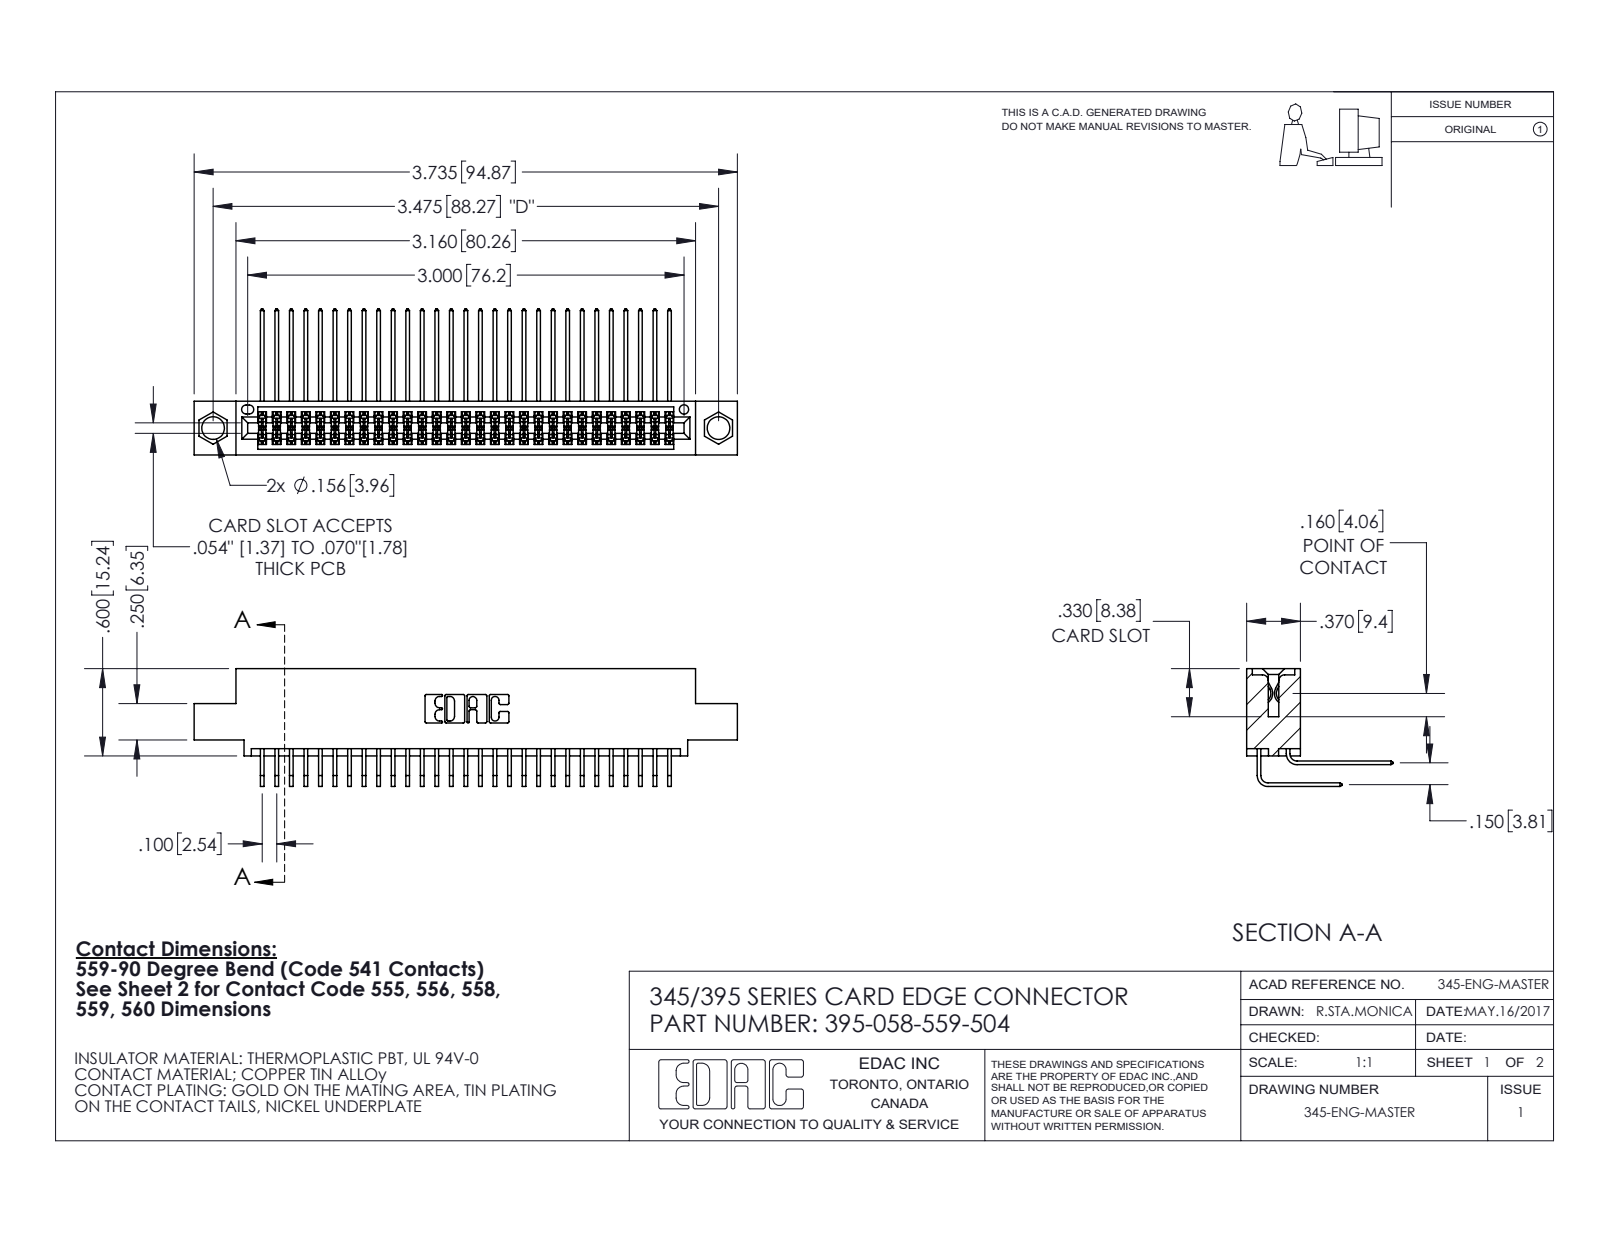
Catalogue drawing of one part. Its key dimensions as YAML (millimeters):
part_name: "395-058-559-504; 345-292-001_558 559 Tail - 1; 345-292-001_559 Tail - 2; 345 Part_0.110 Offset - 0.156 Dia-TI"
step_written_by: "SolidWorks 2020 (CONFIG_CONTROL_DESIGN)"
units: millimeters
bodies: {solids: 59, faces: 3160, planar: 2128, cylindrical: 1032, other: 0}
overall_size: [94.9, 25.5, 20.5]
volume: 9240
surface_area: 14940
round_holes:
  - {diameter: 4, count: 2}
  - {diameter: 1.6, count: 1}
partial_cylinders:
  - {radius: 0.2, count: 87}
  - {radius: 0.3, count: 22}
  - {radius: 0.2, count: 6}
  - {radius: 0.8, count: 6}
  - {radius: 0.7, count: 3}
  - {radius: 0.4, count: 2}
  - {radius: 0.5, count: 2}
  - {radius: 0.6, count: 2}
face_to_face_distances: [1.8, 7.6, 5.1, 9.4, 2.5, 6.9, 0.6, 5.7, 3.8, 4.4]
hole_center_spacings: [6.9, 82.3, 88.3]
